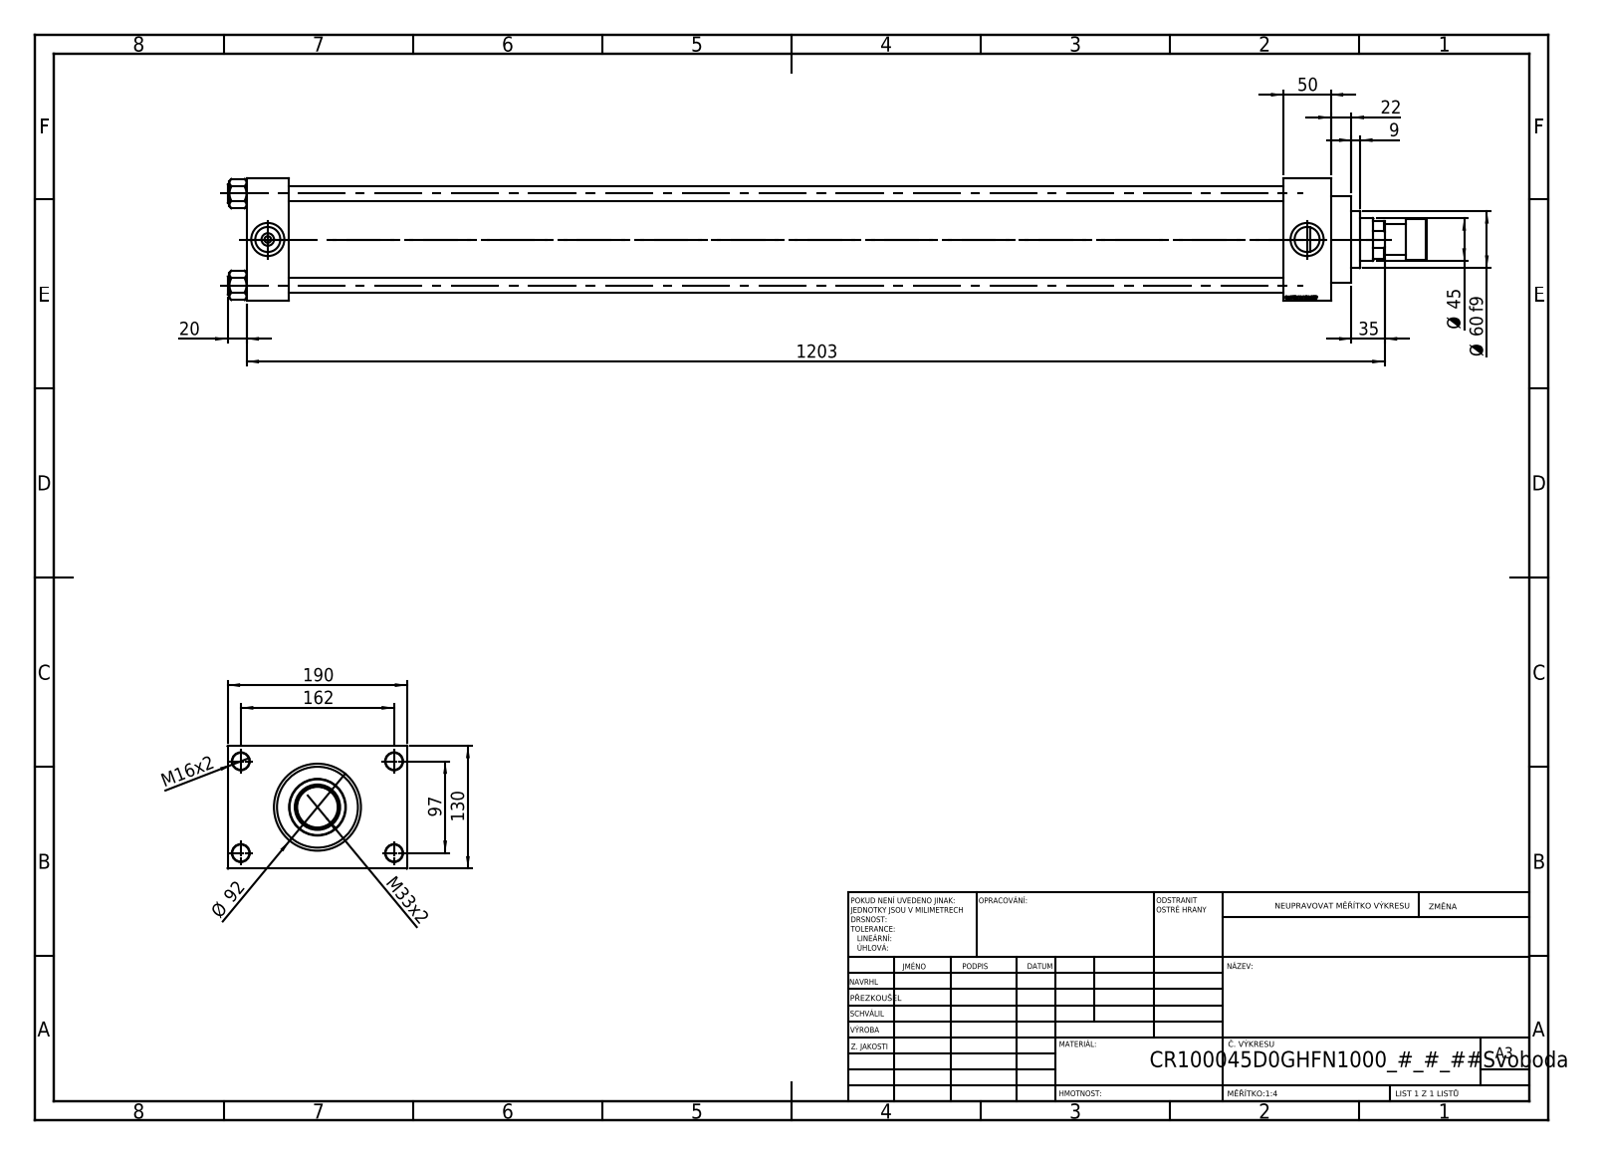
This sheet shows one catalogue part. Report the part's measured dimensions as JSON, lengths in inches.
{"part_name": "V215CR_VCP_D; V215_VC_A; NUT_M5_D; V215CR_D_TYCINKA (+2 more)", "step_written_by": "SolidWorks 2019 (CONFIG_CONTROL_DESIGN)", "units": "inches", "bodies": {"solids": 12, "faces": 1164, "planar": 548, "cylindrical": 92, "other": 524}, "overall_size": [49.882, 7.48, 5.118], "volume_in3": 362.5, "surface_area_in2": 2066, "round_holes": [[0.63, 4], [0.709, 4], [0.276, 2], [1.041, 2], [1.378, 2], [1.24, 1], [1.772, 1], [1.89, 1], [2.992, 1], [3.366, 1], [3.937, 1]], "round_bosses_or_shafts": [[0.748, 4], [4.173, 1], [3.622, 1], [2.362, 1], [1.732, 1], [1.299, 1]], "face_to_face_distances": [5.118, 1.772, 43.15, 41.378, 45.118, 43.346, 1.969, 1.181, 6.299, 3.78], "hole_center_spacings": [1.281, 2.698, 3.717, 3.815, 4.026, 5.096, 6.367, 3.819]}
